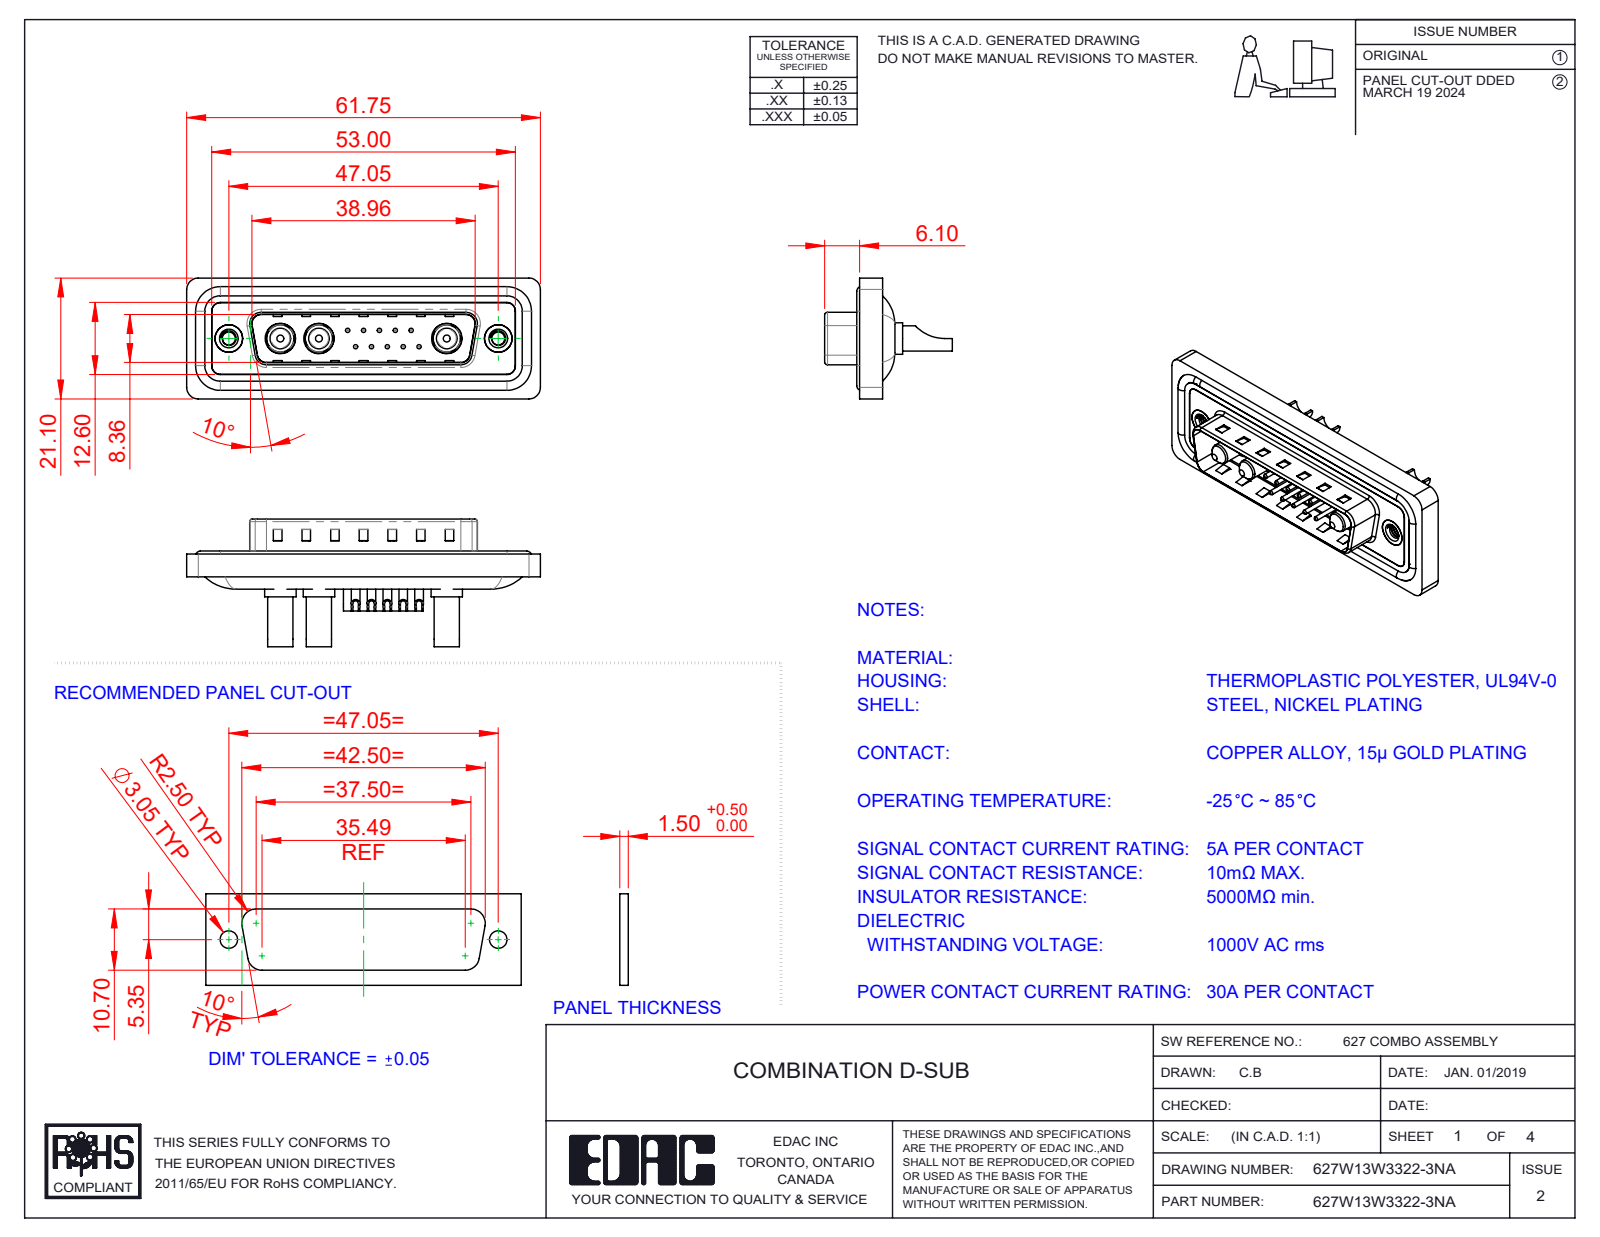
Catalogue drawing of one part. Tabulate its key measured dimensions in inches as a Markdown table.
| quantity | value |
| --- | --- |
| part name | 627Combo Housing_13W3; 627Combo Contact Row 2_22; 627W13W3322-3NA; 627Combo Shell Front_25 Contacts (+5 more) |
| STEP written by | SolidWorks 2023 (CONFIG_CONTROL_DESIGN) |
| units | inches |
| bodies | 23 solids, 986 faces (338 planar, 416 cylindrical, 232 other) |
| overall size | 2.431 × 0.878 × 0.831 |
| volume | 0.453 in³ |
| surface area | 19.03 in² |
| round holes (diameter × count) | 0.03 × 10, 0.039 × 10, 0.063 × 10, 0.079 × 10, 0.138 × 3, 0.191 × 3, 0.209 × 3, 0.089 × 2, 0.157 × 2, 0.189 × 2, 0.197 × 2 |
| round bosses / shafts (diameter × count) | 0.059 × 10, 0.063 × 4, 0.217 × 3, 0.205 × 3, 0.187 × 3, 0.173 × 3, 0.148 × 3, 0.142 × 3 |
| partial cylindrical surfaces (radius × count) | 0.059 × 22, 0.079 × 18, 0.02 × 8, 0.063 × 8, 0.039 × 6, 0.01 × 4, 0.024 × 4, 0.026 × 4 |
| main face-to-face distances | 0.016, 0.059, 0.043, 0.063, 0.02, 0.122, 0.114, 0.032, 0.377, 0.161 |
| hole center spacings | 0.124, 0.109, 0.198, 0.218, 0.295, 0.198, 0.327, 0.398 |
